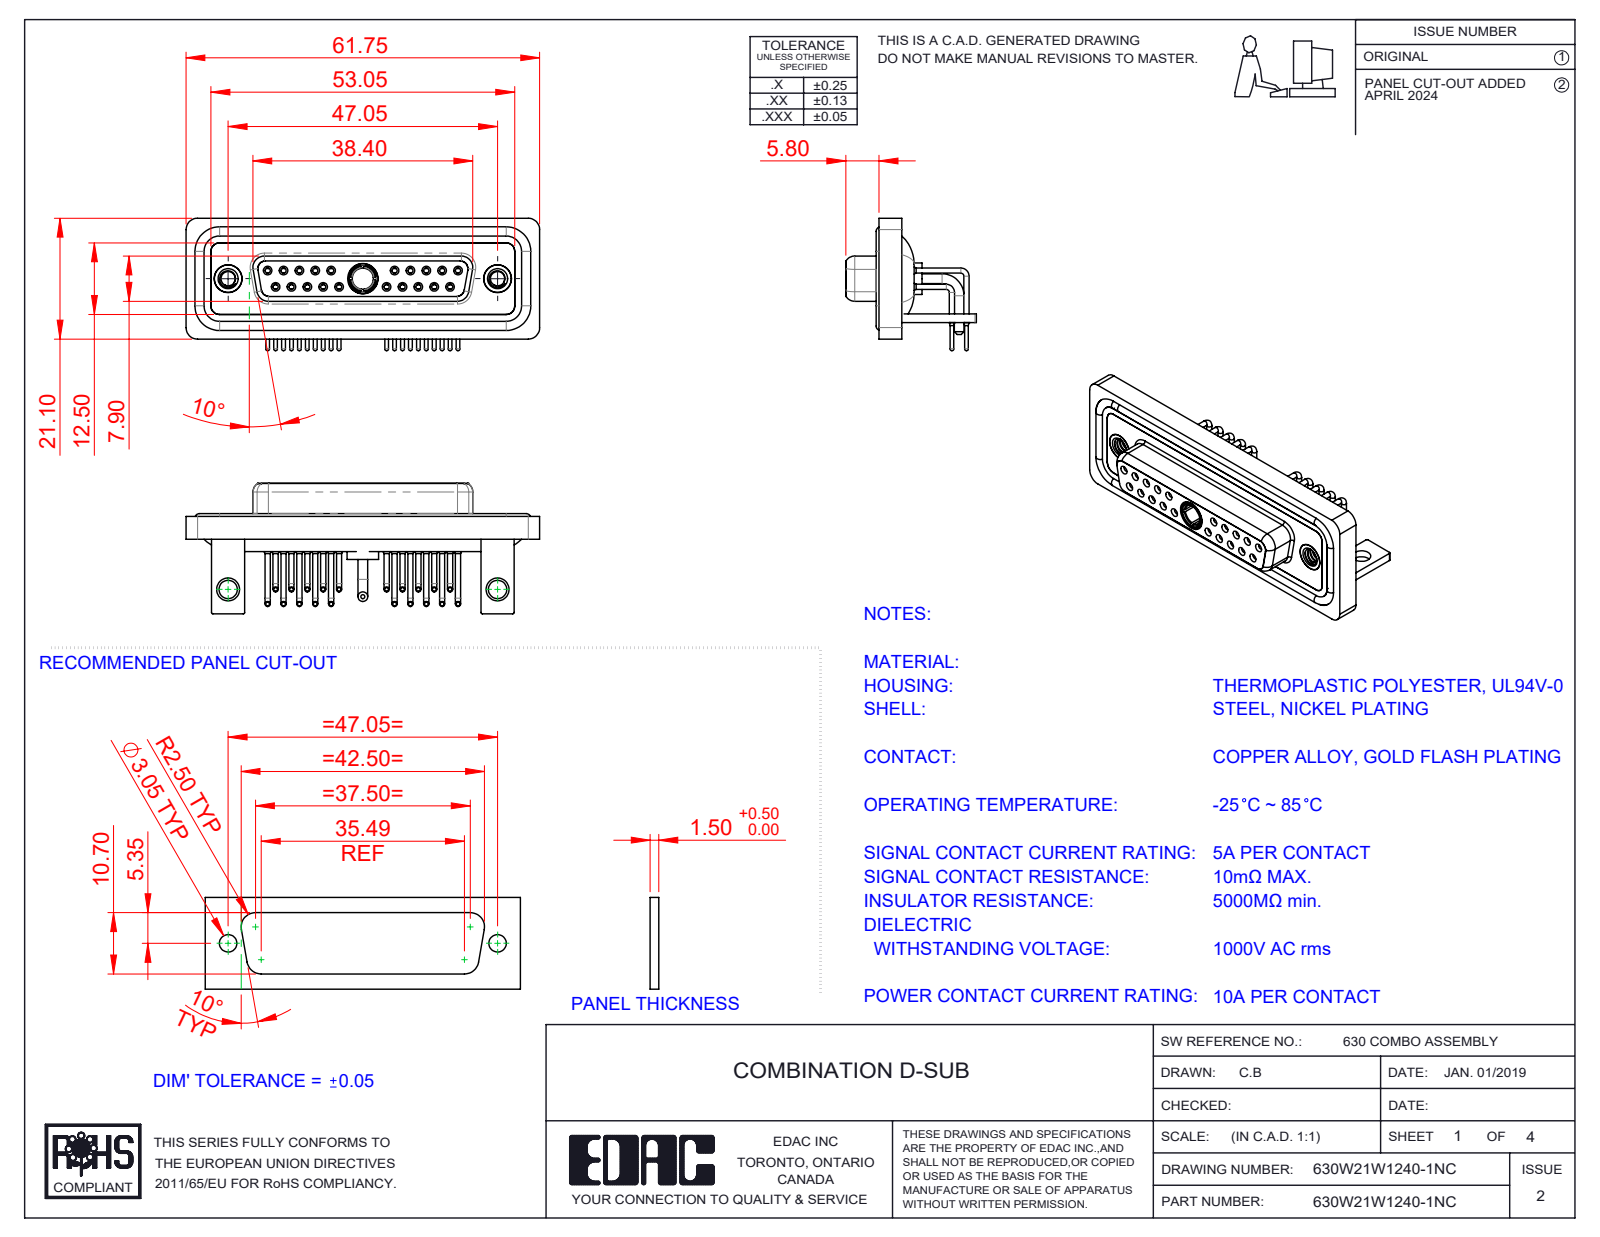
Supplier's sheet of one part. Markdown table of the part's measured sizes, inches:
| quantity | value |
| --- | --- |
| part name | 630Combo Contact Row 2_50 Contacts; 630Combo Threaded Rivet_A; 630Combo Shell Rear_25 Contacts; 630Combo Contact Row 1_50 Contacts (+6 more) |
| STEP written by | SolidWorks 2023 (CONFIG_CONTROL_DESIGN) |
| units | inches |
| bodies | 31 solids, 1566 faces (454 planar, 695 cylindrical, 417 other) |
| overall size | 2.431 × 0.91 × 0.898 |
| volume | 0.537 in³ |
| surface area | 23.98 in² |
| round holes (diameter × count) | 0.035 × 20, 0.043 × 20, 0.059 × 20, 0.079 × 20, 0.063 × 10, 0.067 × 10, 0.191 × 3, 0.098 × 2, 0.126 × 2, 0.157 × 2, 0.159 × 2, 0.197 × 2 |
| round bosses / shafts (diameter × count) | 0.035 × 20, 0.026 × 20, 0.063 × 14, 0.195 × 2, 0.189 × 2, 0.067 × 2, 0.217 × 1, 0.205 × 1 |
| partial cylindrical surfaces (radius × count) | 0.079 × 19, 0.059 × 18, 0.01 × 16, 0.053 × 8, 0.063 × 8, 0.02 × 5, 0.024 × 4, 0.026 × 4 |
| main face-to-face distances | 0.016, 0.071, 0.114, 0.146, 0.059, 0.161, 0.043, 0.055, 0.063, 0.098 |
| hole center spacings | 0.124, 0.109, 0.218, 0.327, 0.198, 0.763, 0.826, 0.872 |
